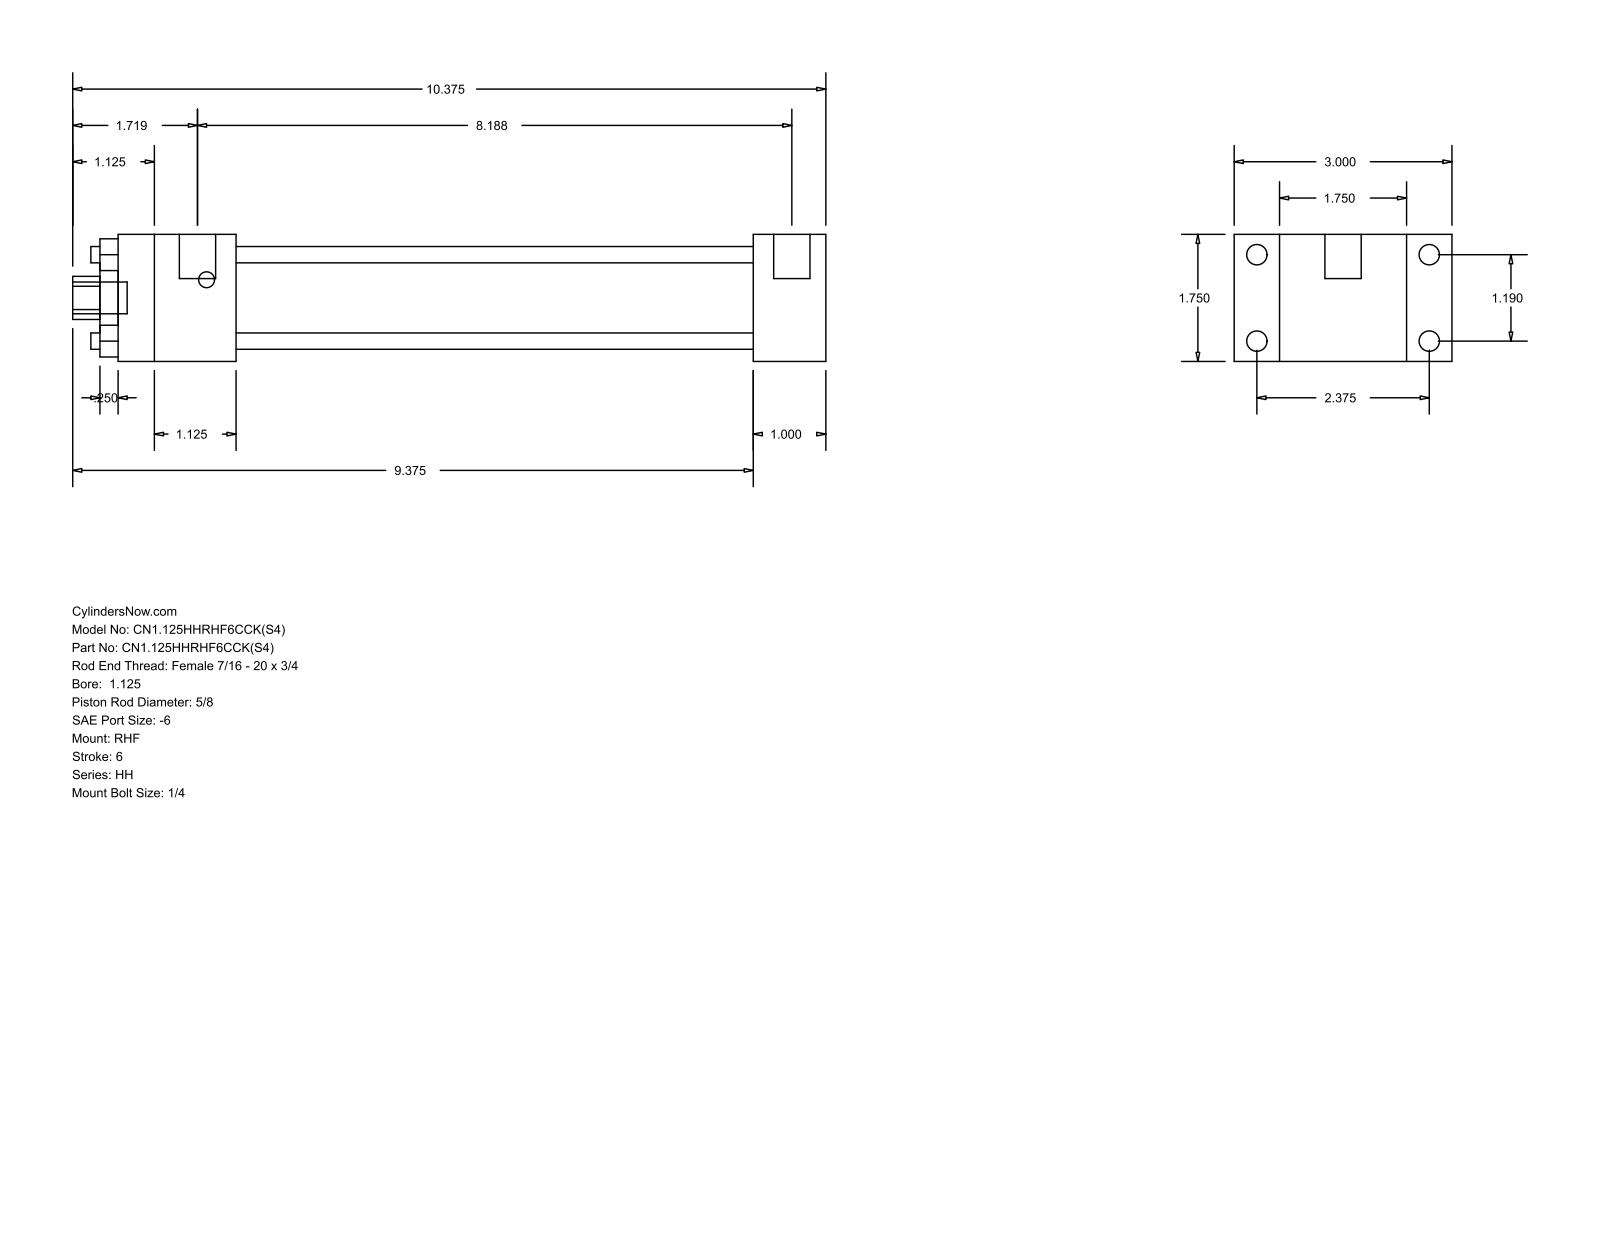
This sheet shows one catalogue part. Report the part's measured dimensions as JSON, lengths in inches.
{"part_name": "HH_RHF__0112_0.625", "step_written_by": "GSSL Pune (CONFIG_CONTROL_DESIGN)", "units": "inches", "bodies": {"solids": 0, "faces": 88, "planar": 60, "cylindrical": 28, "other": 0}, "overall_size": [10.375, 3, 1.75], "round_holes": [[0.225, 4], [0.625, 1], [1.125, 1], [1.375, 1]], "round_bosses_or_shafts": [[0.281, 4], [0.219, 4], [0.5, 2], [0.437, 1]], "partial_cylinders_radius": [[0.297, 1]], "face_to_face_distances": [1.75, 0.625, 2.375, 1, 3, 7.125, 8.125, 1.625, 8.75, 9.75], "hole_center_spacings": [0.841, 1.19, 1.683]}
